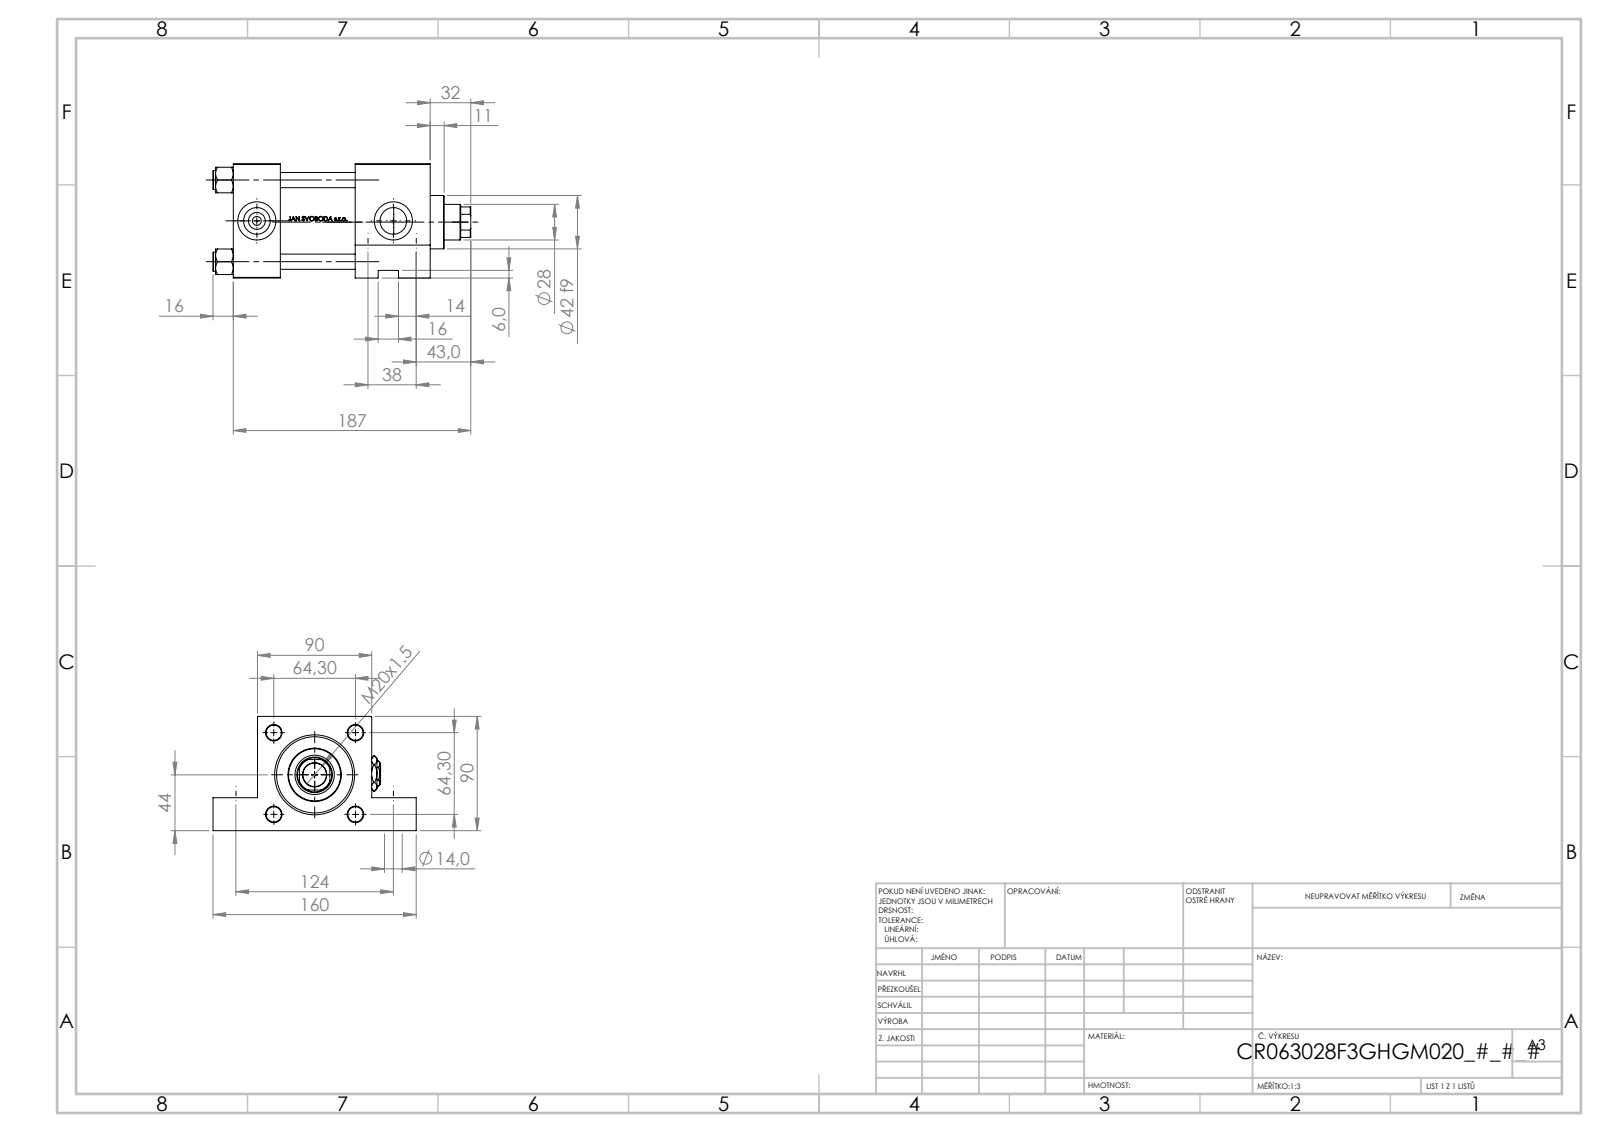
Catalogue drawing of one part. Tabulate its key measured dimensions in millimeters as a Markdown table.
| quantity | value |
| --- | --- |
| part name | V215CR_F_Body; V215CR_VCP_F; Zatka_pro_OIL_PORT; V215_VC_A (+2 more) |
| STEP written by | SolidWorks 2019 (CONFIG_CONTROL_DESIGN) |
| units | millimeters |
| bodies | 13 solids, 1218 faces (488 planar, 148 cylindrical, 582 other) |
| overall size | 203 × 160 × 90 |
| volume | 1 013 000 mm³ |
| surface area | 198 995 mm² |
| round holes (diameter × count) | 12 × 4, 18 × 4, 20.96 × 3, 30 × 3, 2.5 × 2, 7 × 2, 18.5 × 1, 20 × 1, 28 × 1, 31 × 1, 50 × 1, 60 × 1 |
| round bosses / shafts (diameter × count) | 15 × 4, 69 × 1, 42 × 1 |
| partial cylindrical surfaces (radius × count) | 13.5 × 1 |
| main face-to-face distances | 90, 59, 37, 118, 155, 96, 20, 125, 64, 26 |
| hole center spacings | 32.39, 45.47, 64.3, 68.42, 28.25, 38, 90.93, 124 |
